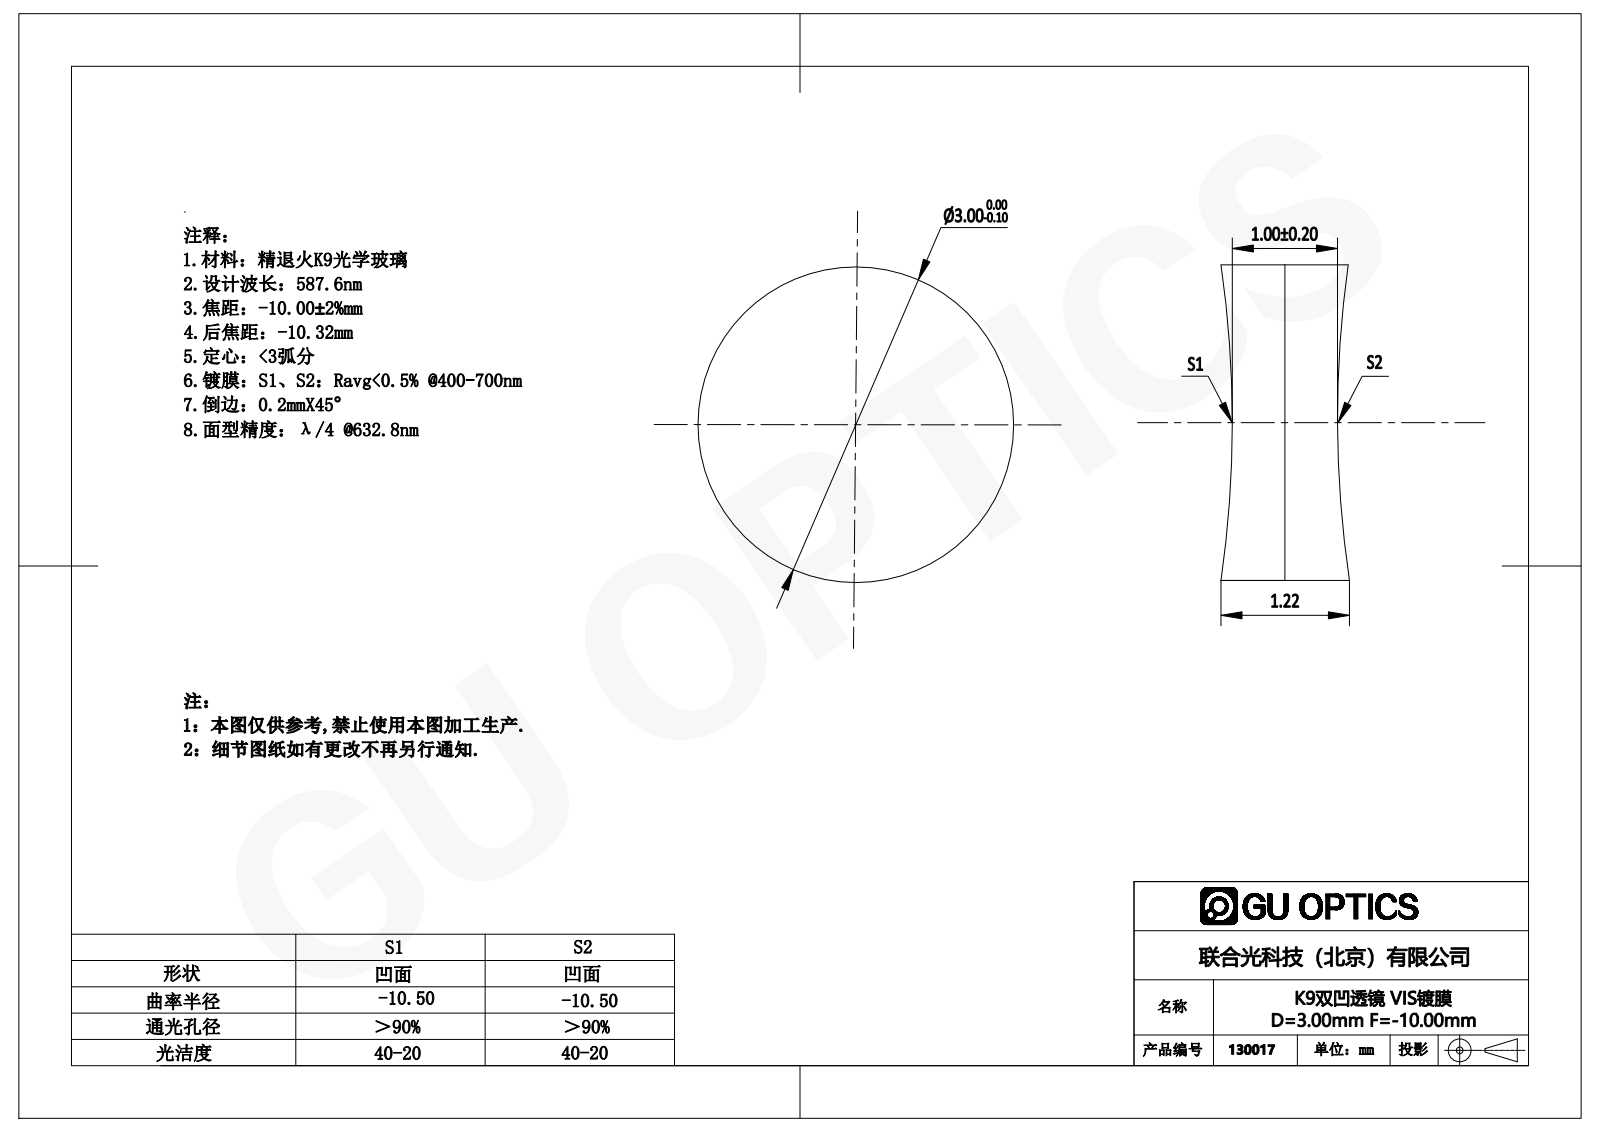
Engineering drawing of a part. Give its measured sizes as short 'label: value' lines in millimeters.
name: 130004
written by: SolidWorks 2016 (AUTOMOTIVE_DESIGN)
unit: mm
bodies: 1 solid, 6 faces (0 planar, 2 cylindrical, 4 other)
size: 3 × 3 × 1.21
volume: 8 mm³; area: 26 mm²
bosses: 1× ⌀3
